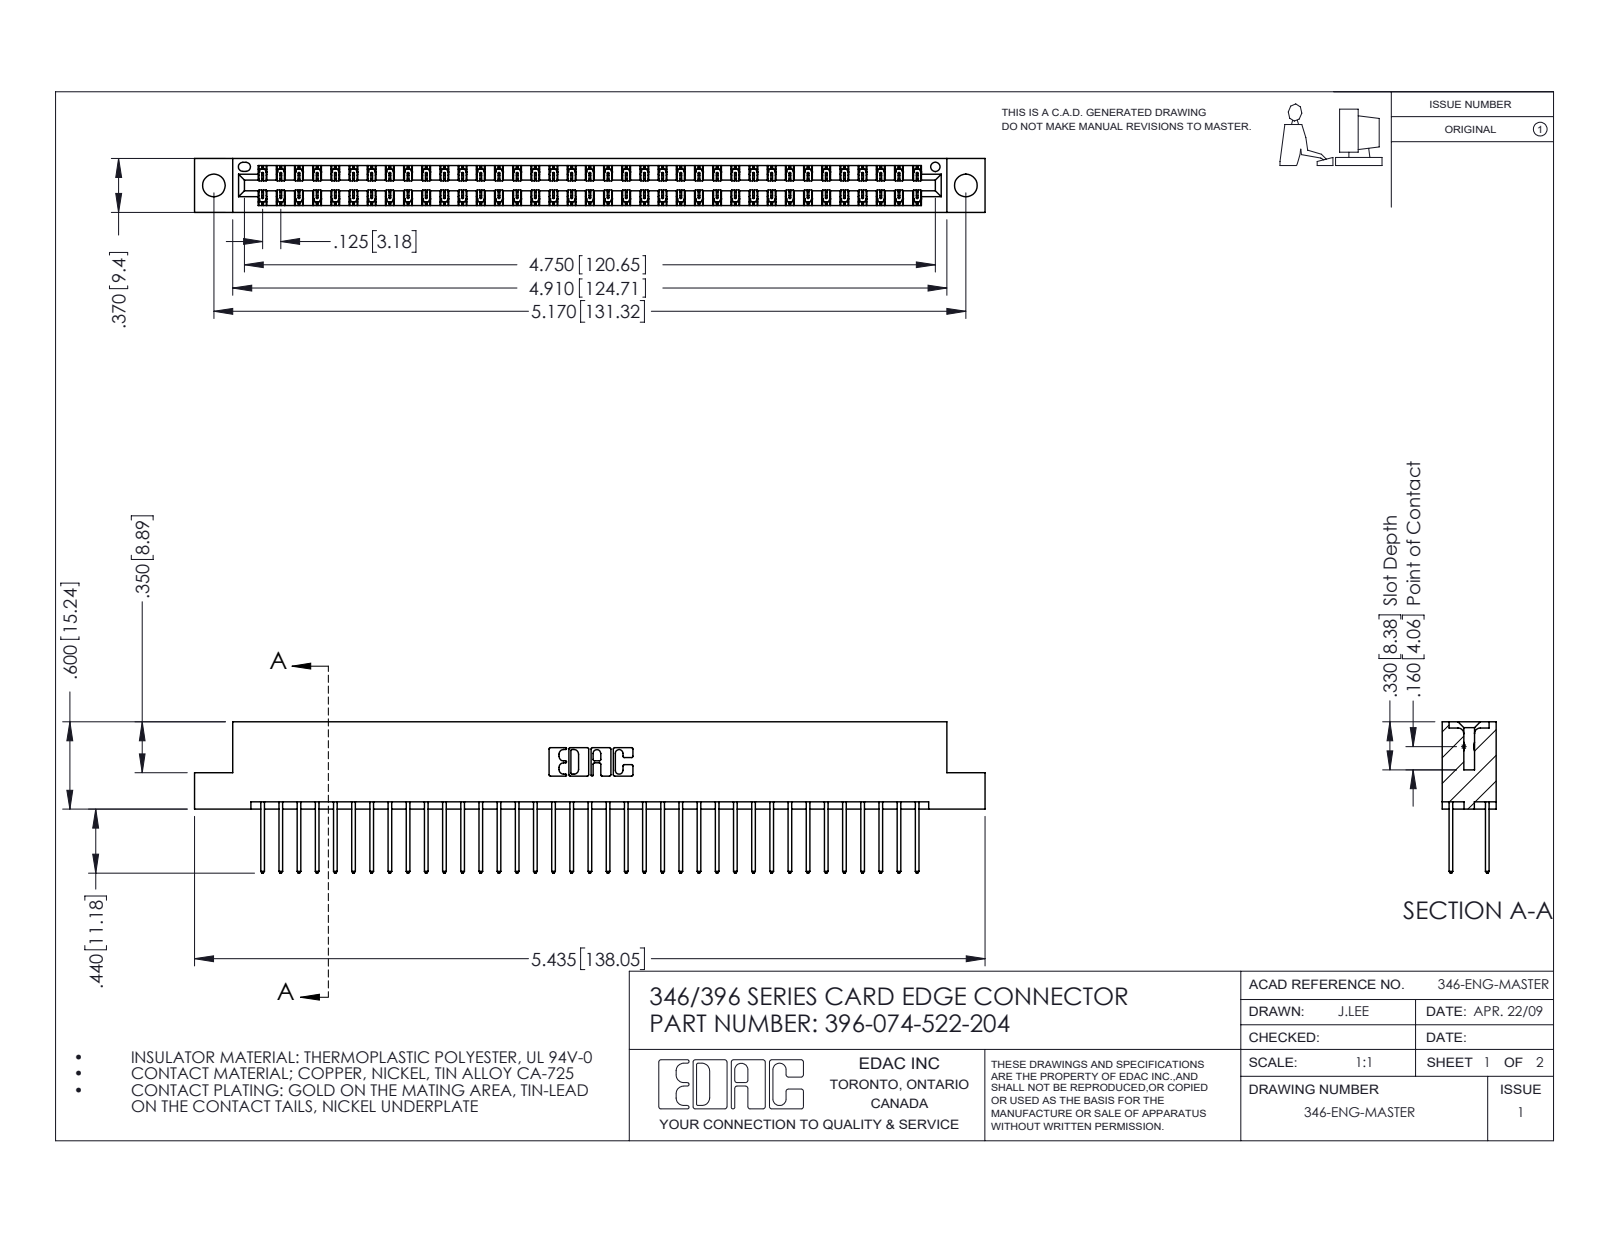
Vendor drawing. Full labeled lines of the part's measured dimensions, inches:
Part name (STEP PRODUCT): 345-292-001_345-293-122; 346 Part_Flush Mounting Lugs - 0.156 Dia-TH; 396-074-522-204
STEP written by: SolidWorks 2016 (CONFIG_CONTROL_DESIGN)
Units: inches
Bodies: 75 solids, 3970 faces (2666 planar, 1304 cylindrical, 0 other)
Overall size (bounding box): 5.435 × 1.04 × 0.37
Volume: 0.825 in³ · Surface area: 29.77 in²
Round holes (diameter × count): ⌀0.156 ×2, ⌀0.064 ×1
Partial cylindrical surfaces — rounded edges, fillets, slot ends (radius × count): R0.006 ×111, R0.01 ×74, R0.01 ×22, R0.007 ×6, R0.031 ×6, R0.026 ×3, R0.014 ×2, R0.022 ×2
Main face-to-face distances: 0.048, 0.322, 0.25, 0.37, 0.072, 0.298, 0.025, 0.275, 0.148, 0.222
Hole centre spacings: 0.246, 4.961, 5.17
